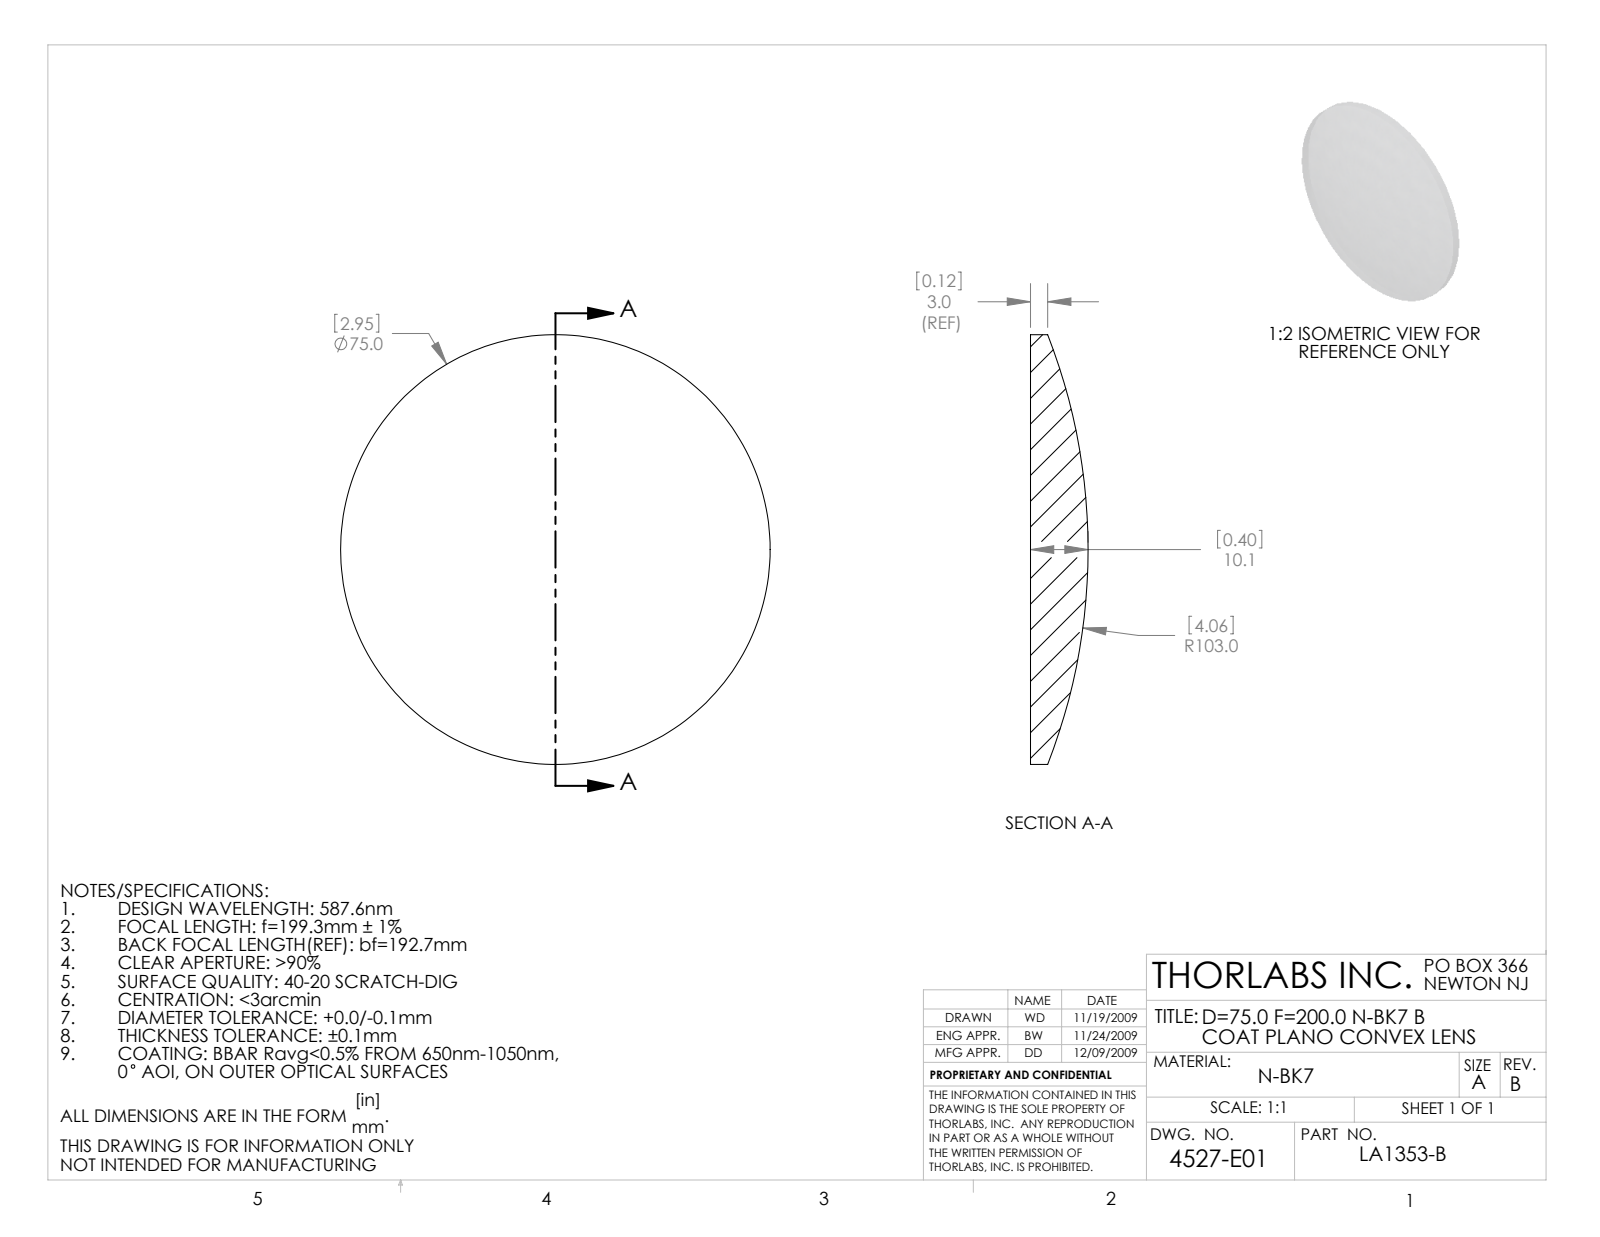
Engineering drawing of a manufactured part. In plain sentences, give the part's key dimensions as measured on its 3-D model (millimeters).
The part is named "4527-E0W". Its 3-D file was written by "SolidWorks 2009 (AUTOMOTIVE_DESIGN)". It is 1 solid with 5 faces: 1 planar, 2 cylindrical and 2 other. Overall it measures 75 by 75 by 10.06 millimeters. Its volume is 29 015 cubic millimeters and its surface area 9 698 square millimeters. Round bosses or shafts: 1 of diameter 75.
